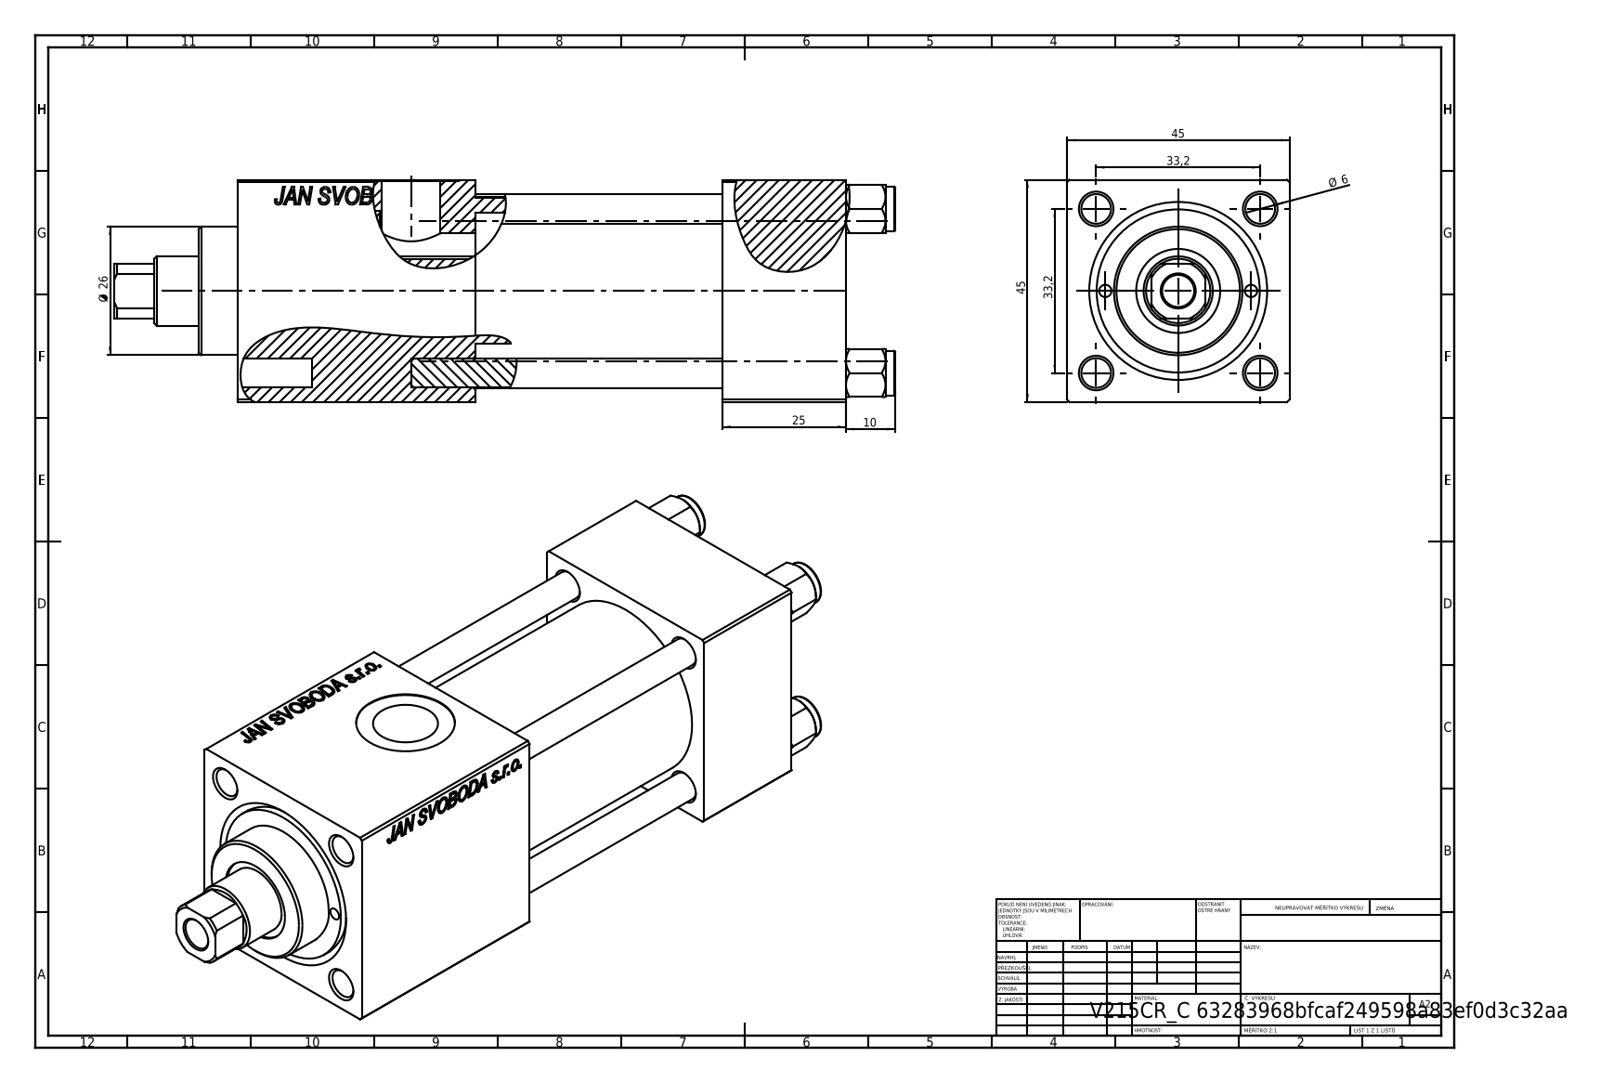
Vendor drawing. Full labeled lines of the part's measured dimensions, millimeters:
Part name (STEP PRODUCT): V215CR_C_Body; V215CR_VCP_C; V215CR_C_TYCINKA; NUT_M5_C (+1 more)
STEP written by: SolidWorks 2019 (CONFIG_CONTROL_DESIGN)
Units: millimetres
Bodies: 11 solids, 1154 faces (527 planar, 91 cylindrical, 536 other)
Overall size (bounding box): 158 × 45 × 45
Volume: 193 777 mm³ · Surface area: 67 162 mm²
Round holes (diameter × count): ⌀6 ×4, ⌀2.5 ×2, ⌀7 ×2, ⌀13.16 ×2, ⌀20 ×2, ⌀6.5 ×1, ⌀14 ×1, ⌀17 ×1, ⌀24 ×1, ⌀32 ×1, ⌀33 ×1
Round bosses / shafts (diameter × count): ⌀9 ×4, ⌀38 ×1, ⌀26 ×1
Partial cylindrical surfaces — rounded edges, fillets, slot ends (radius × count): R6.5 ×1
Main face-to-face distances: 45, 25, 98, 123, 50, 75, 48, 94.3, 69.3, 19.3
Hole centre spacings: 16.7, 23.48, 33.2, 35.47, 14.75, 46.95, 29.5, 75.5
